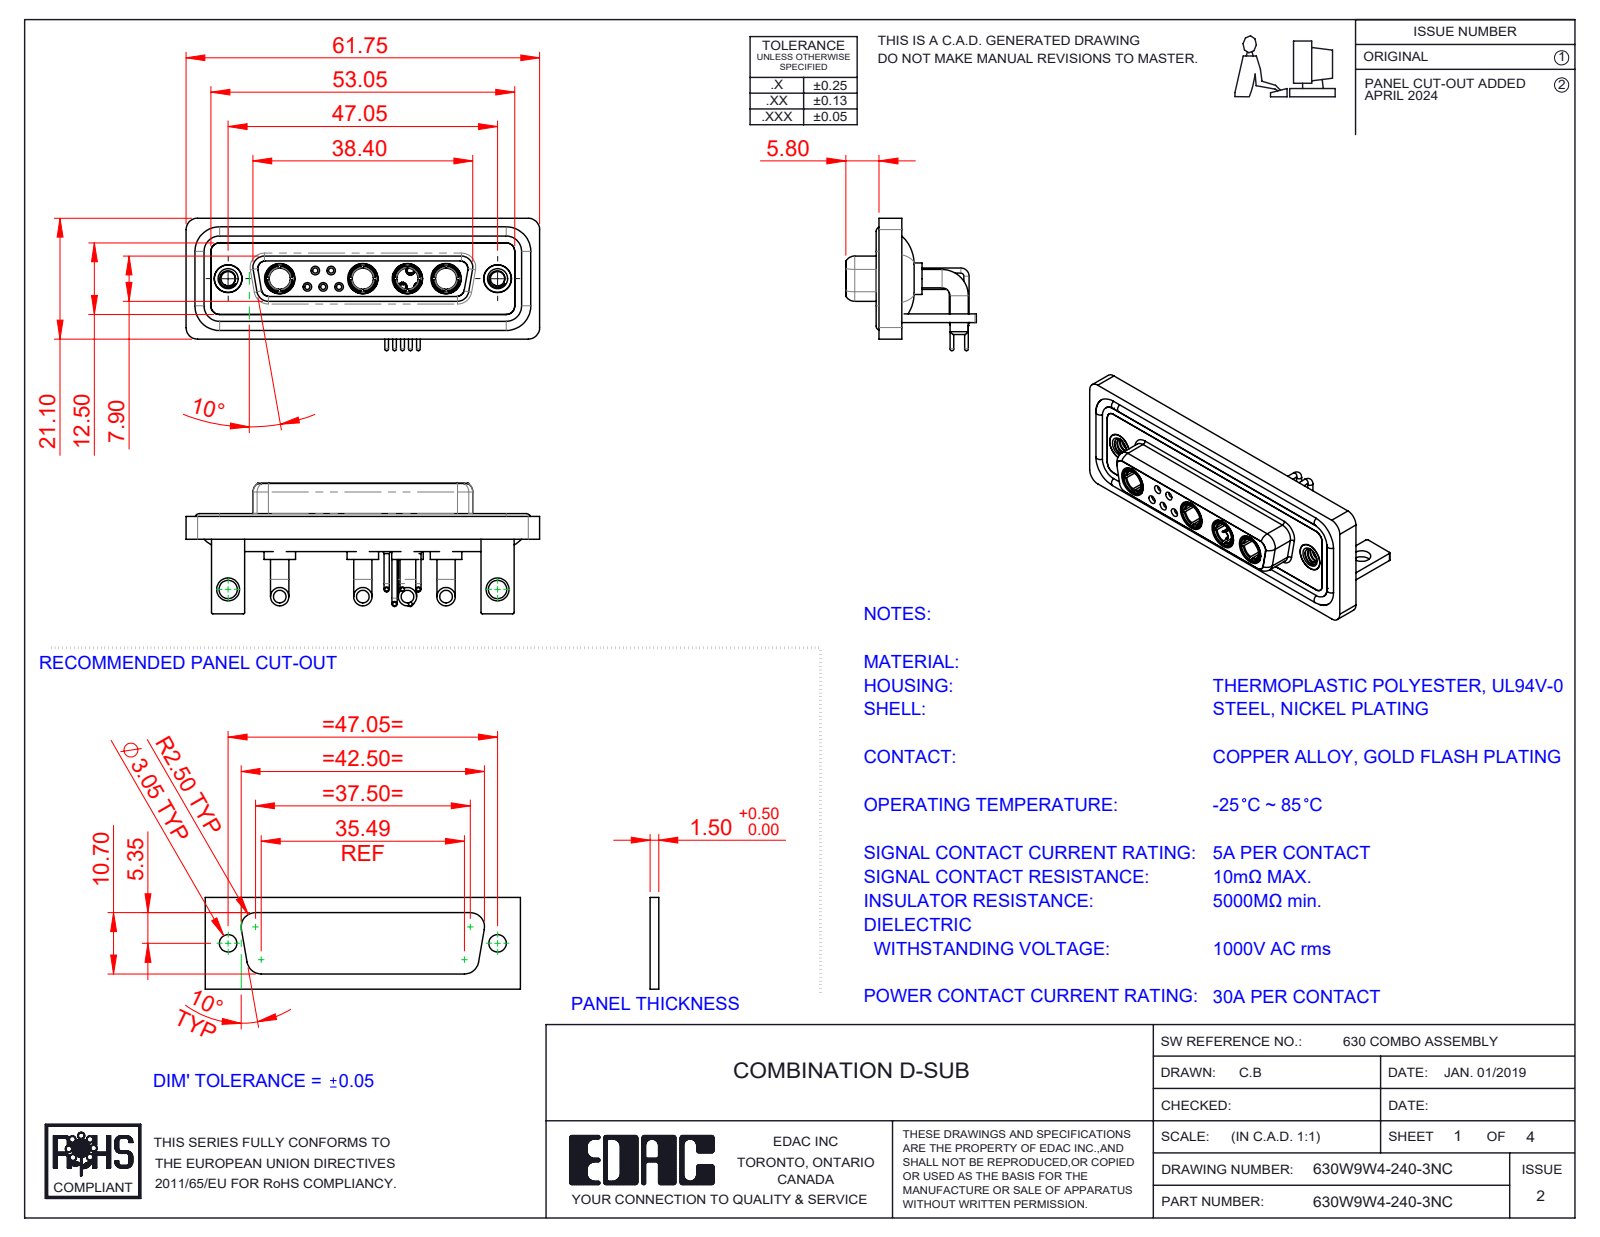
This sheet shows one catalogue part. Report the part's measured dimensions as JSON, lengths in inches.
{"part_name": "630Combo Waterproof Housing_25 Contacts; 630Combo Shell Rear_25 Contacts; 630Combo Contact Row 2_50 Contacts; 630Combo Contact Row 1_50 Contacts (+6 more)", "step_written_by": "SolidWorks 2023 (CONFIG_CONTROL_DESIGN)", "units": "inches", "bodies": {"solids": 22, "faces": 1005, "planar": 316, "cylindrical": 425, "other": 264}, "overall_size": [2.431, 0.91, 0.898], "volume_in3": 0.545, "surface_area_in2": 23.03, "round_holes": [[0.191, 6], [0.035, 5], [0.043, 5], [0.059, 5], [0.079, 5], [0.146, 4], [0.209, 4], [0.063, 3], [0.067, 2], [0.098, 2], [0.126, 2], [0.157, 2]], "round_bosses_or_shafts": [[0.035, 10], [0.063, 9], [0.126, 8], [0.079, 5], [0.059, 5], [0.026, 5], [0.217, 4], [0.205, 4]], "partial_cylinders_radius": [[0.079, 19], [0.059, 18], [0.01, 16], [0.053, 8], [0.063, 8], [0.02, 5], [0.024, 4], [0.026, 4]], "face_to_face_distances": [0.016, 0.071, 0.114, 0.146, 0.059, 0.161, 0.043, 0.055, 0.063, 0.098], "hole_center_spacings": [0.124, 0.109, 0.198, 0.545, 0.436, 0.504, 0.61, 0.218]}
